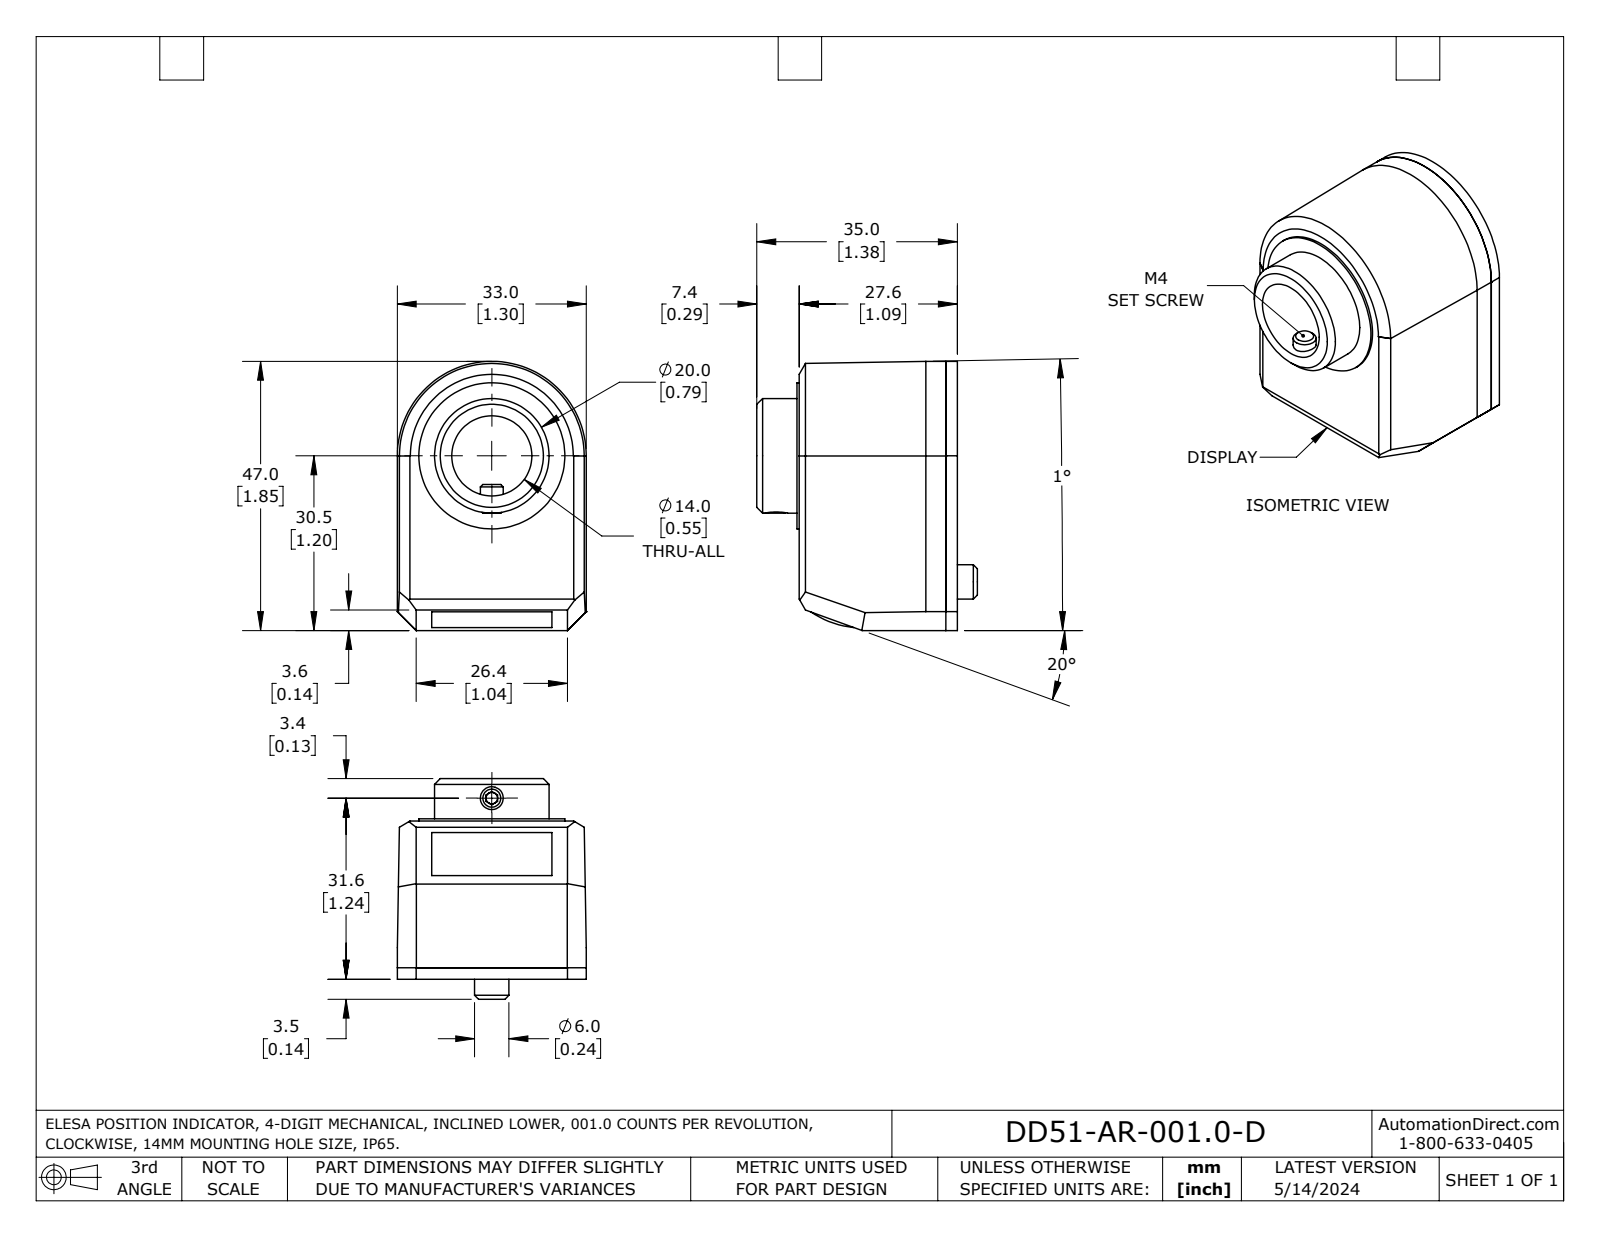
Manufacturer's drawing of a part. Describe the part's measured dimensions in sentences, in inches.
The part is named "DD51-AR-METRIC". Its 3-D file was written by "SolidWorks 2023 (AUTOMOTIVE_DESIGN)". It is 4 solids with 85 faces: 66 planar, 12 cylindrical and 7 other. Overall it measures 1.85 by 1.516 by 1.299 inches. Its volume is 1.994 cubic inches and its surface area 20.33 square inches. Round holes: 1 of diameter 0.157, 1 of diameter 0.551, 1 of diameter 0.787, 1 of diameter 1.083. Round bosses or shafts: 1 of diameter 1.004, 1 of diameter 0.236. Partial cylindrical surfaces (rounded edges, fillets, slot ends): 1 of radius 0.64, 1 of radius 0.65. The main face-to-face distances are 0.079, 0.078, 1.008, 1.008, 1.087, 0.138, 0.217, 0.87, 0.138, 1.299.
